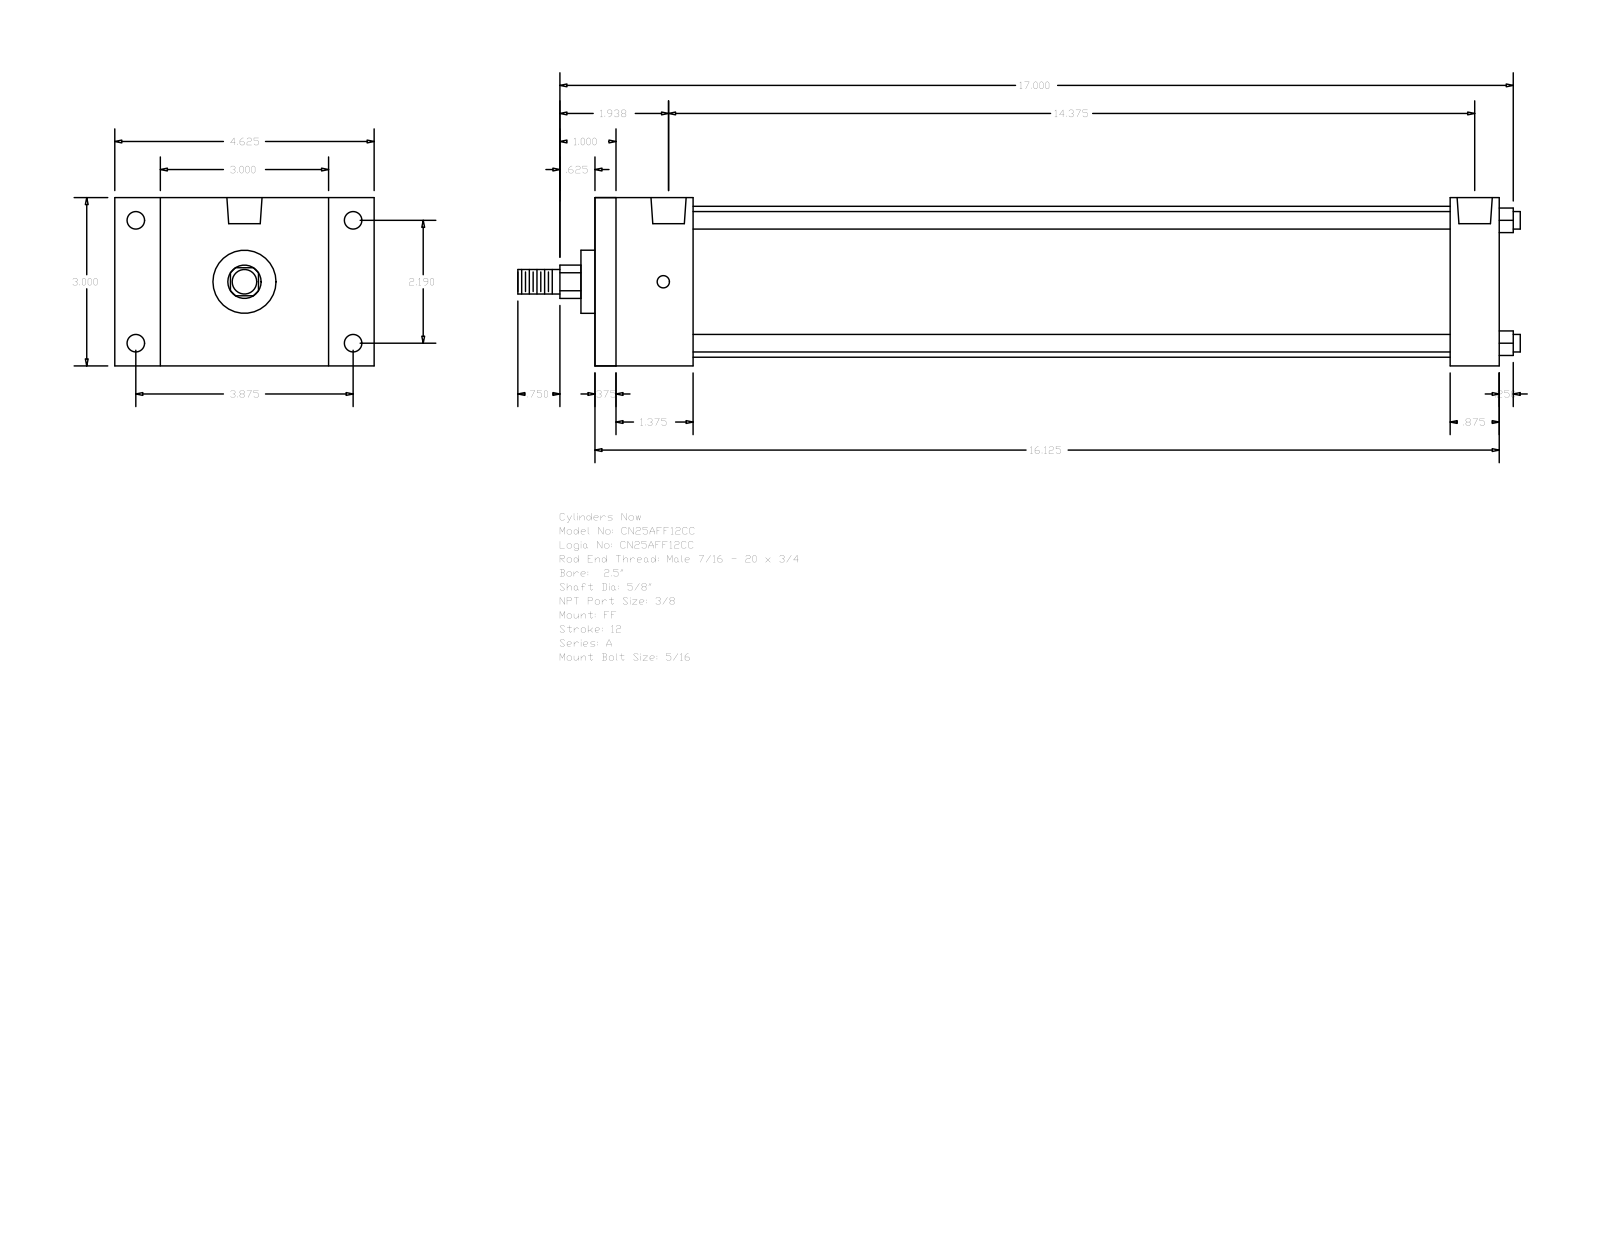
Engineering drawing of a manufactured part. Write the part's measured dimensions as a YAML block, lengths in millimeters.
part_name: "A_FF__0250_0.625"
step_written_by: "GSSL Pune (CONFIG_CONTROL_DESIGN)"
units: millimeters
bodies: {solids: 0, faces: 92, planar: 64, cylindrical: 28, other: 0}
overall_size: [454.02, 117.47, 76.2]
round_holes:
  - {diameter: 5.56, count: 4}
  - {diameter: 7.94, count: 4}
  - {diameter: 15.93, count: 2}
round_bosses_or_shafts:
  - {diameter: 7.94, count: 4}
  - {diameter: 68.33, count: 1}
  - {diameter: 28.57, count: 1}
  - {diameter: 15.88, count: 1}
  - {diameter: 11.11, count: 1}
partial_cylinders:
  - {radius: 7.54, count: 1}
face_to_face_distances: [76.2, 409.57, 9.52, 400.05, 44.45, 34.93, 387.35, 377.83, 342.9, 365.12]
hole_center_spacings: [2.38, 55.62, 98.42, 113.05, 367.51, 369.89, 365.13]
